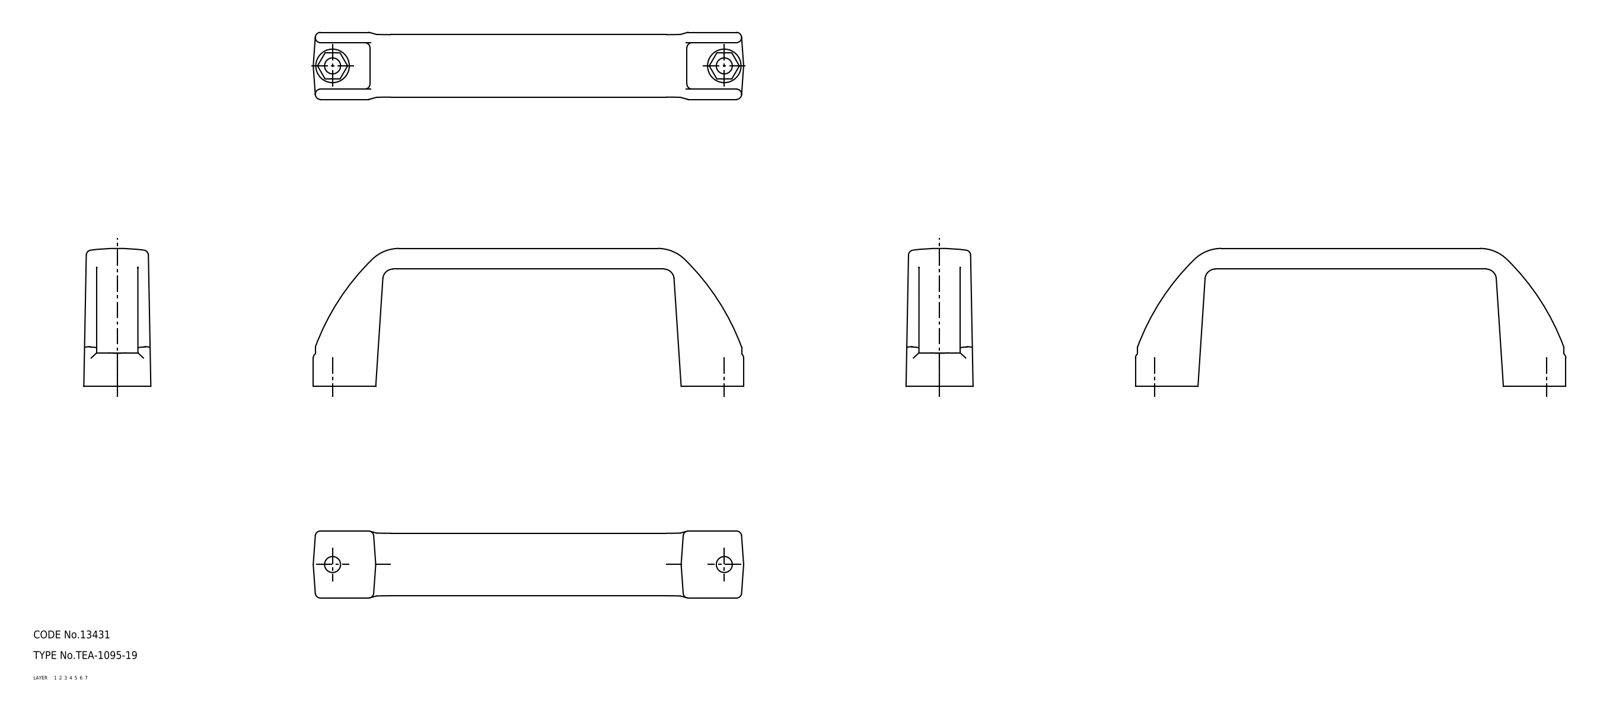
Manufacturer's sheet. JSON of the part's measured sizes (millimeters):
{"part_name": "handle", "step_written_by": "CADfix (AUTOMOTIVE_DESIGN)", "units": "millimeters", "bodies": {"solids": 1, "faces": 100, "planar": 0, "cylindrical": 0, "other": 100}, "overall_size": [167, 53.5, 26], "volume_mm3": 47728, "surface_area_mm2": 19207}
